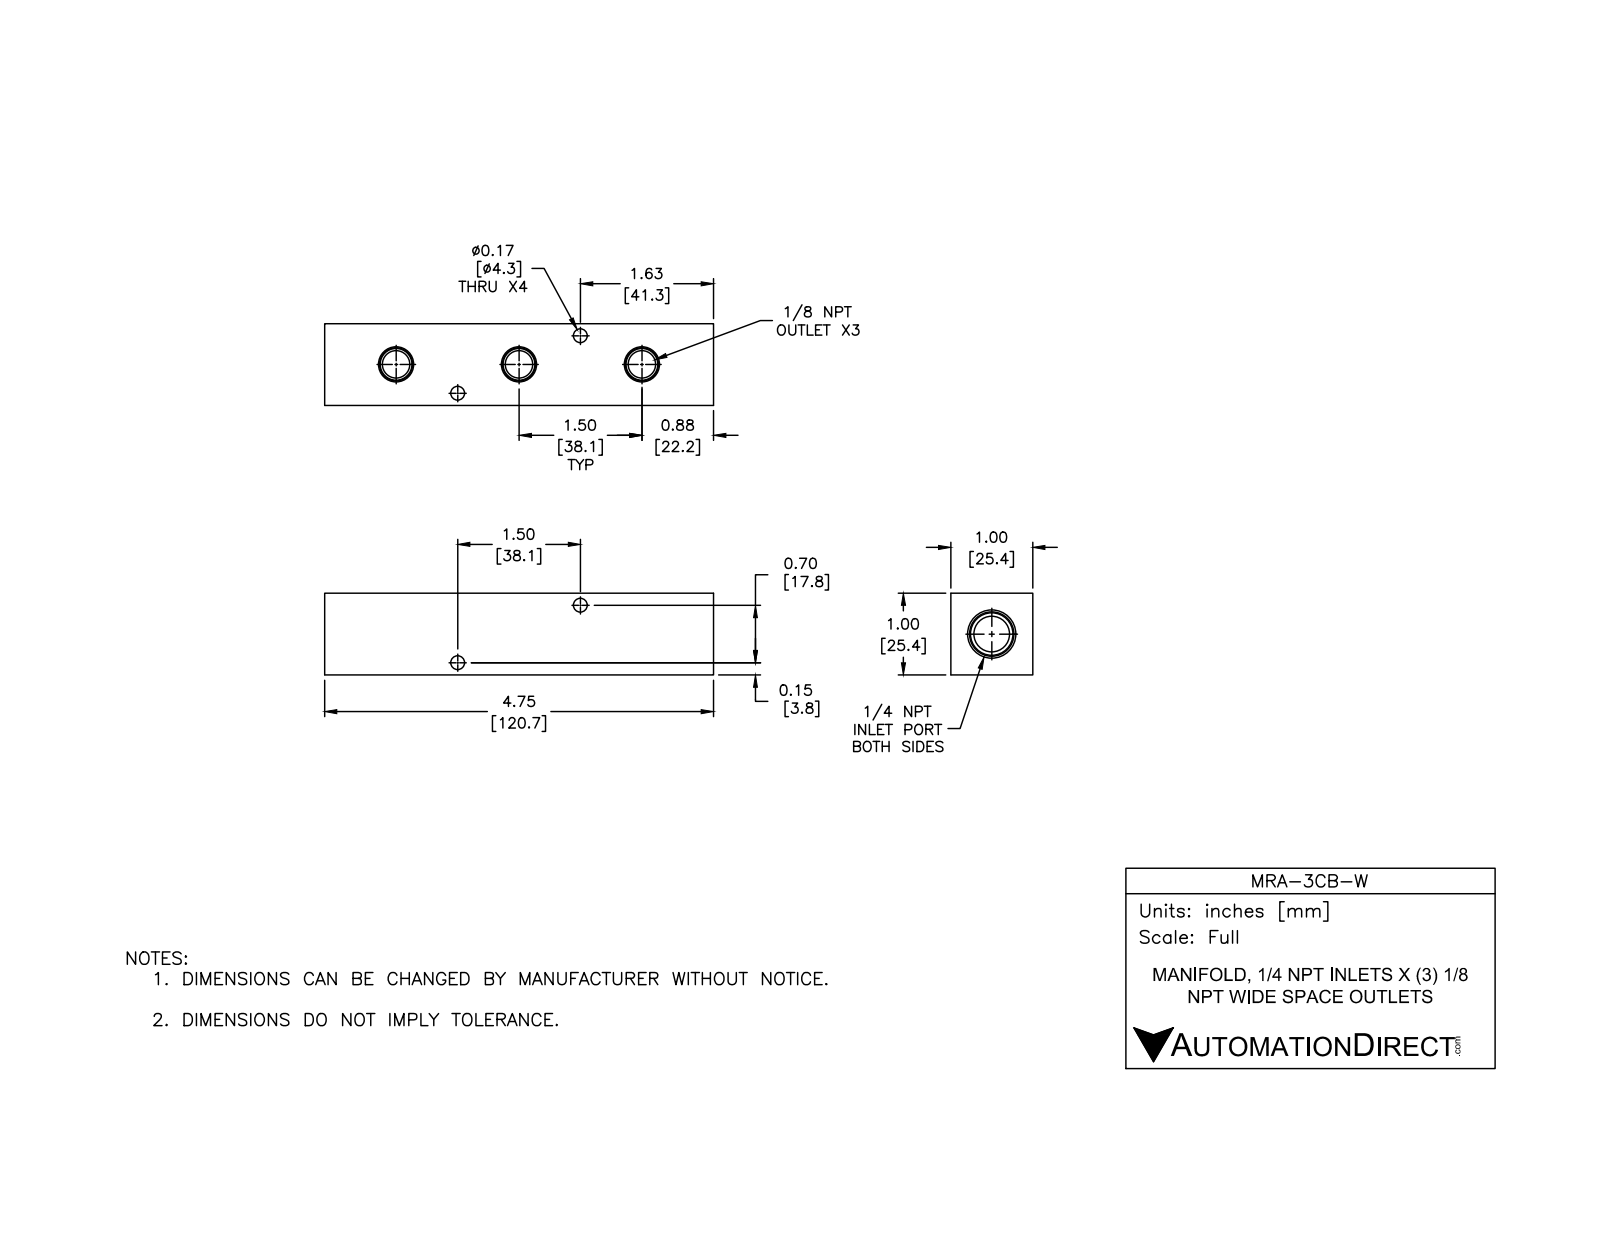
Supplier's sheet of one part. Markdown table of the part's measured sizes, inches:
| quantity | value |
| --- | --- |
| part name | MRA-3CB-W |
| STEP written by | SolidWorks 2015 (CONFIG_CONTROL_DESIGN) |
| units | inches |
| bodies | 1 solid, 55 faces (11 planar, 24 cylindrical, 20 other) |
| overall size | 4.75 × 1 × 1 |
| volume | 3.787 in³ |
| surface area | 29.66 in² |
| round holes (diameter × count) | 0.17 × 4, 0.332 × 3, 0.438 × 1 |
| main face-to-face distances | 1, 4.75, 0.39, 4.36, 0.73, 0.27, 3.97 |
| hole center spacings | 0.828, 1.5, 1.655, 2.277, 3 |
